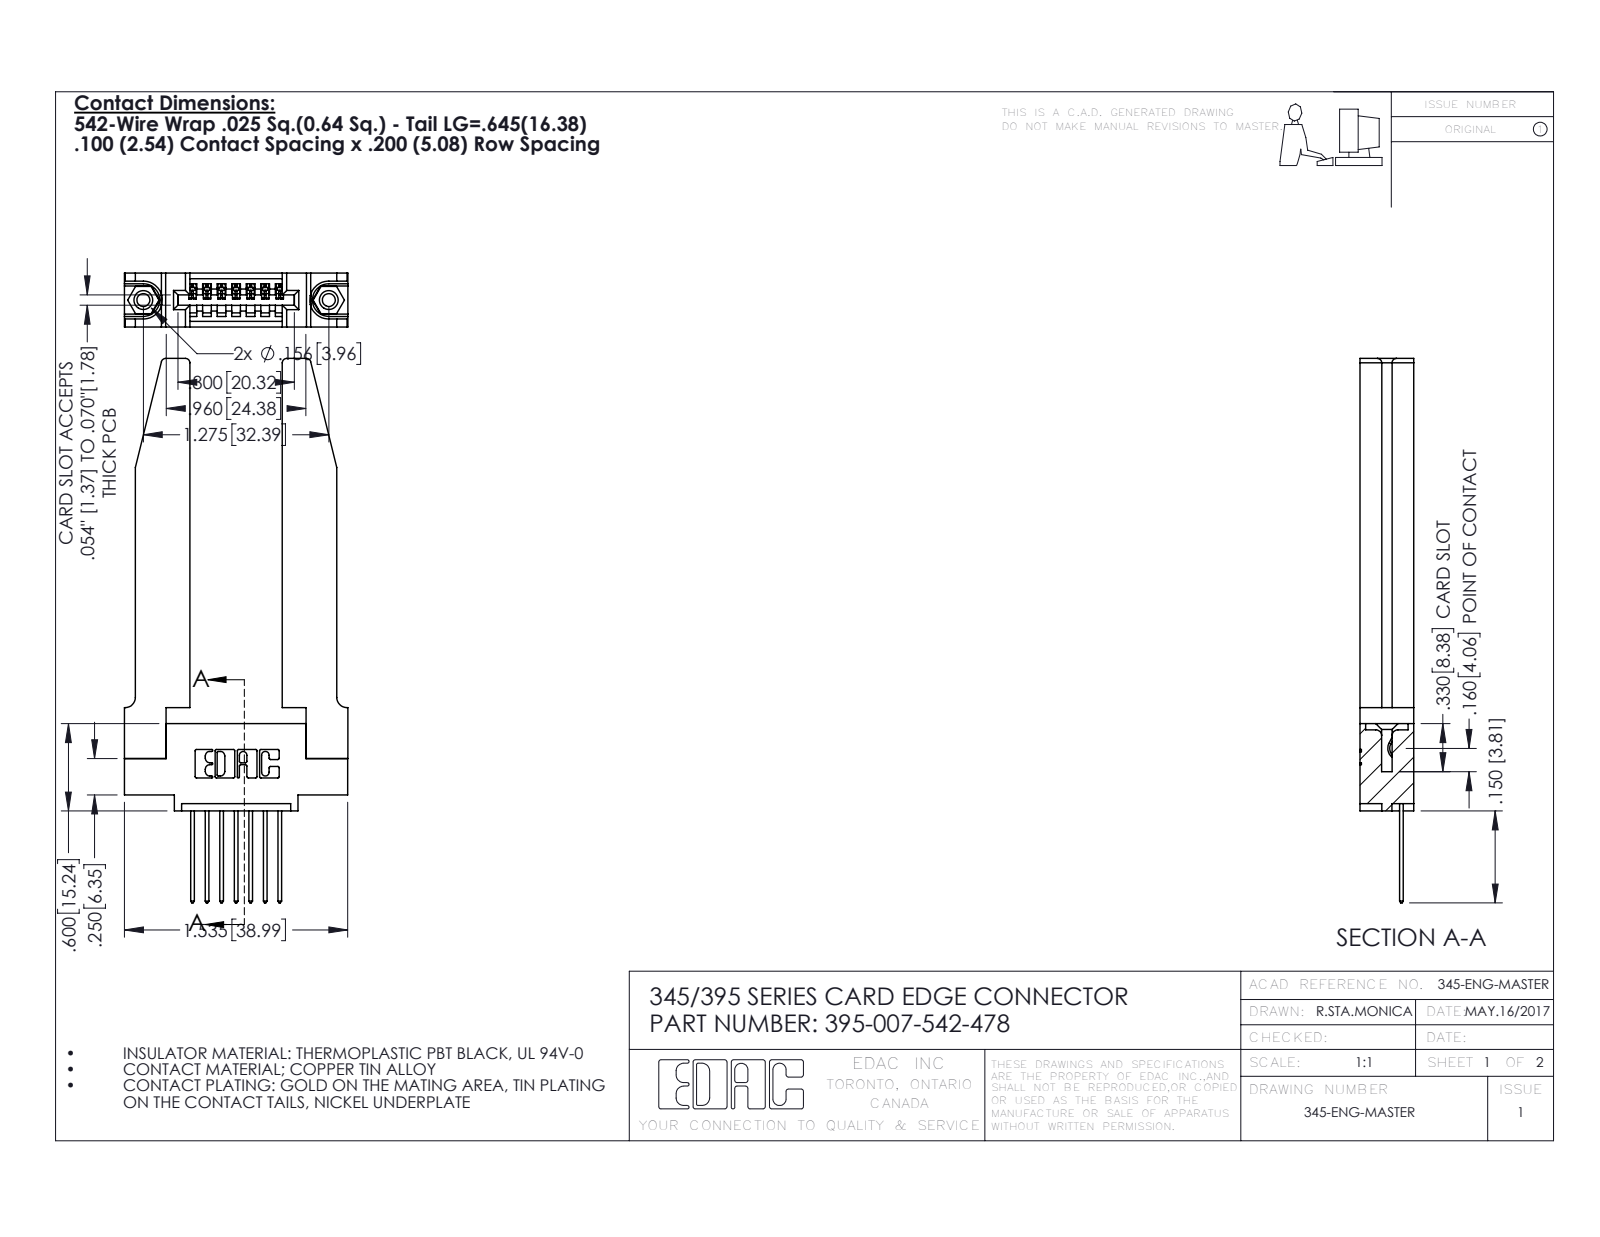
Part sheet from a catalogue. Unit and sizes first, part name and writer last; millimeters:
Units: millimetres
Overall size (bounding box): 95 × 39 × 9.4
Round holes (diameter × count): ⌀2.3 ×2, ⌀3.2 ×2, ⌀4 ×2, ⌀1.6 ×1
Round bosses / shafts (diameter × count): ⌀3.9 ×2
Partial cylindrical surfaces — rounded edges, fillets, slot ends (radius × count): R0.3 ×22, R0.2 ×14, R0.3 ×14, R0.8 ×8, R0.2 ×6, R0.8 ×6, R0.7 ×3, R0.8 ×2
Main face-to-face distances: 9.4, 3.8, 1.8, 5.6, 7.6, 3.8, 16.1, 2, 5.1, 1.8
Hole centre spacings: 6.9, 26.5, 32.4
Volume: 11 100 mm³ · Surface area: 11 020 mm²
Bodies: 12 solids, 770 faces (506 planar, 212 cylindrical, 52 other)
Part name (STEP PRODUCT): 395-007-542-478; 345-250-001_345-250-001-102; 345 Part_0.110 Offset - 0.156 Dia-TH; 345-220-078_345-220-078 (+1 more)
STEP written by: SolidWorks 2016 (CONFIG_CONTROL_DESIGN)
